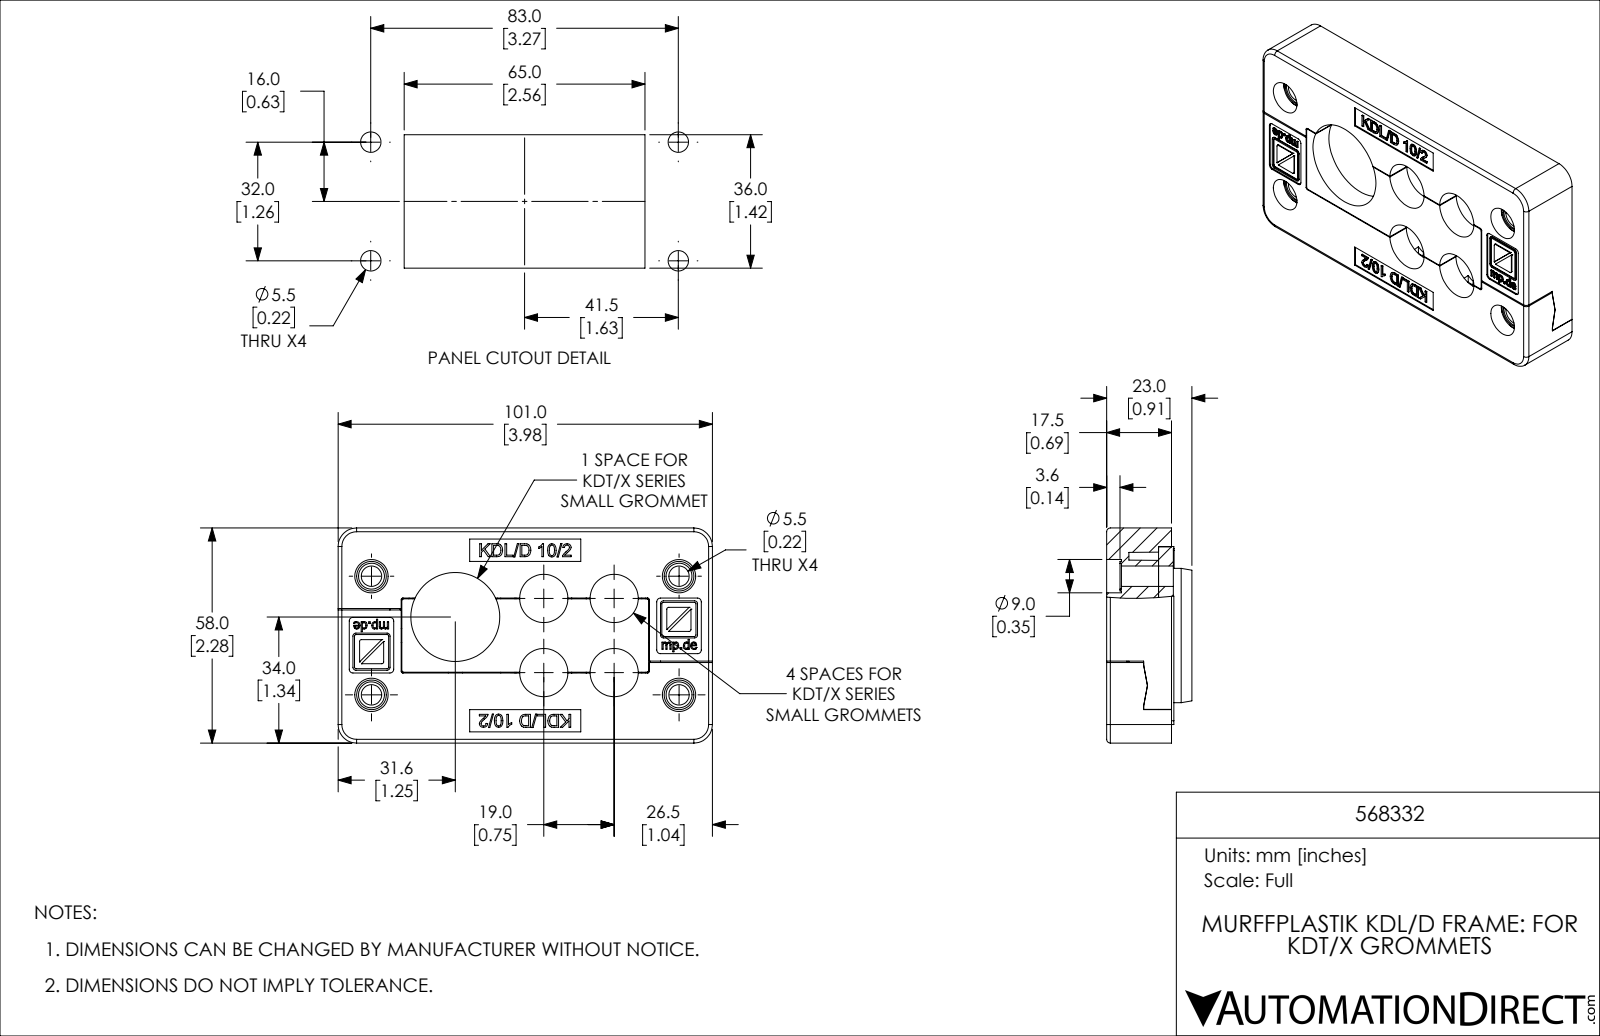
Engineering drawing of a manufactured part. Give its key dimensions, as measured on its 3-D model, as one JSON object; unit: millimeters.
{"part_name": "568332", "step_written_by": "SolidWorks 2019 (CONFIG_CONTROL_DESIGN)", "units": "millimeters", "bodies": {"solids": 4, "faces": 1320, "planar": 748, "cylindrical": 237, "other": 335}, "overall_size": [101, 58, 23], "volume_mm3": 77350, "surface_area_mm2": 42210, "round_holes": [[5, 6], [5.5, 4], [7, 4], [9, 4], [13, 4], [15, 4], [6, 2], [24.9, 1]], "round_bosses_or_shafts": [[8, 4]], "partial_cylinders_radius": [[0.5, 35], [1, 33], [0.4, 12], [0.8, 8], [0.1, 4], [0.2, 4], [0.3, 4], [5, 4]], "face_to_face_distances": [14, 4, 3.5, 5, 6, 12, 0.5, 8, 18, 11.5], "hole_center_spacings": [11.3, 16.7, 11, 7.5, 10, 14.5, 17.5, 18.2]}
